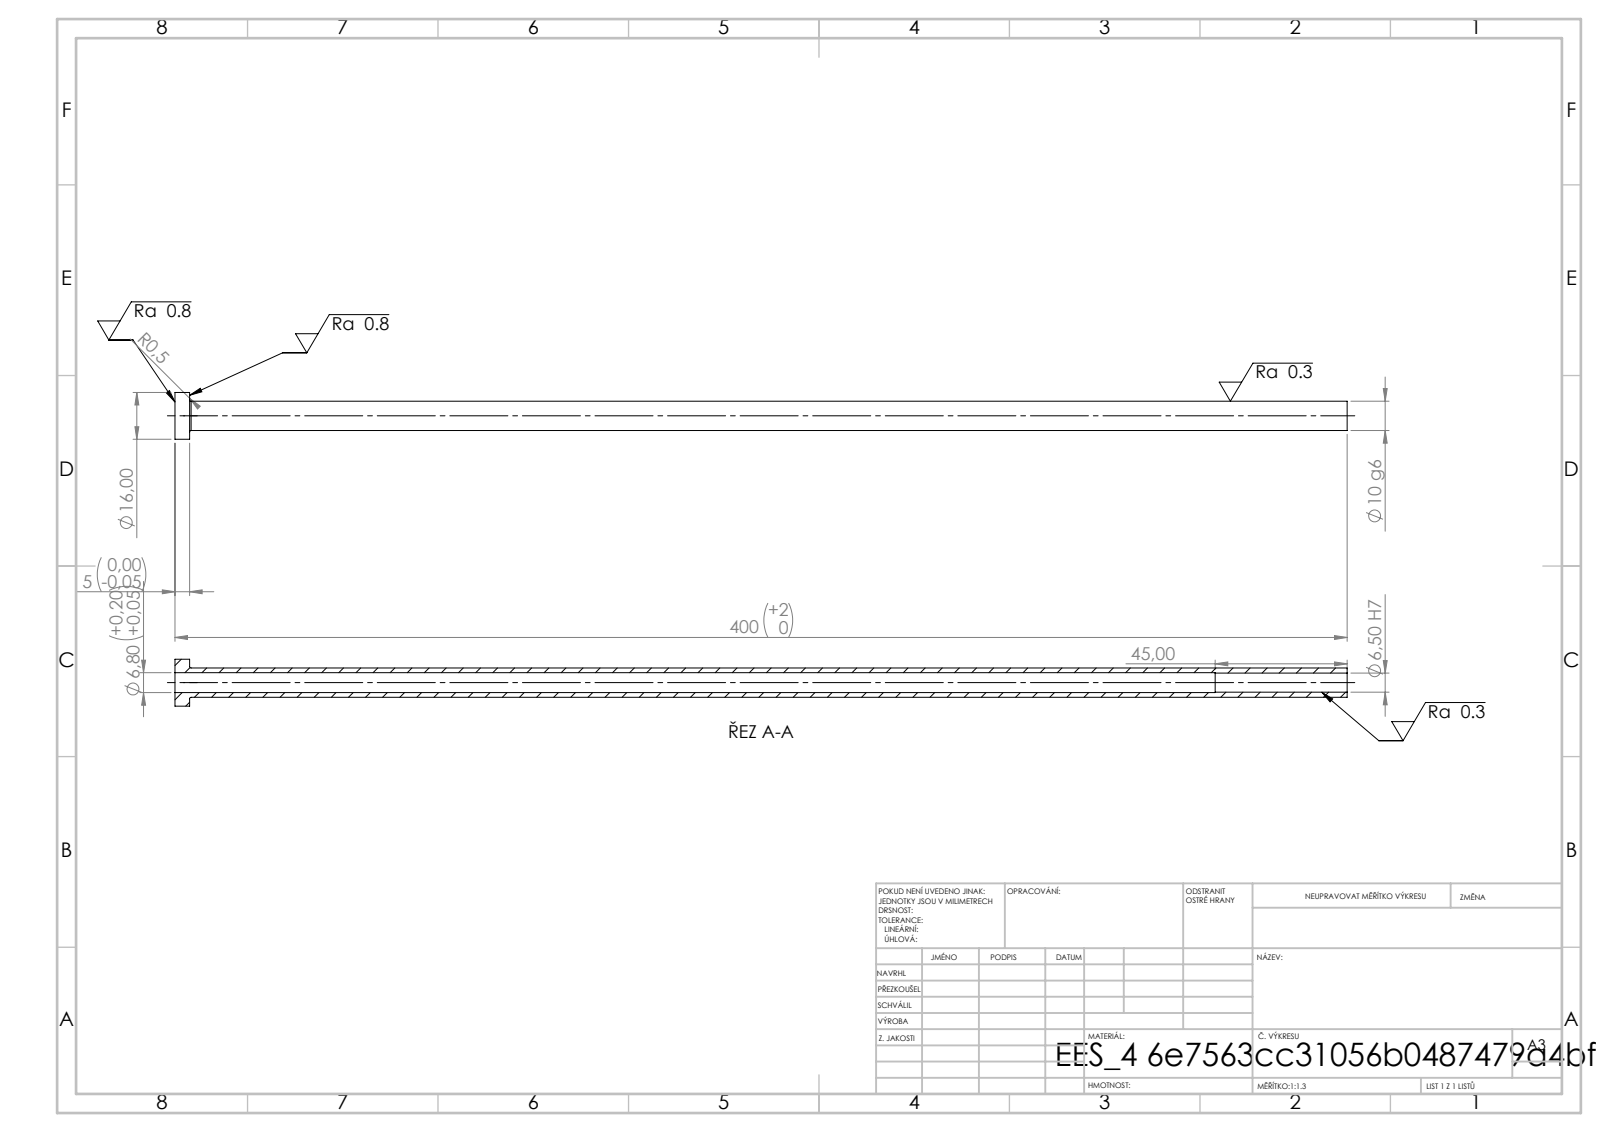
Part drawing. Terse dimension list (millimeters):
written by: SolidWorks 2019 (CONFIG_CONTROL_DESIGN)
unit: mm
bodies: 1 solid, 14 faces (4 planar, 8 cylindrical, 2 other)
size: 400 × 16 × 16
volume: 17 645 mm³; area: 21 492 mm²
holes: 1× ⌀6.5, 1× ⌀6.8
bosses: 1× ⌀16, 1× ⌀10
face distances: 5, 400, 395, 355, 350, 45
